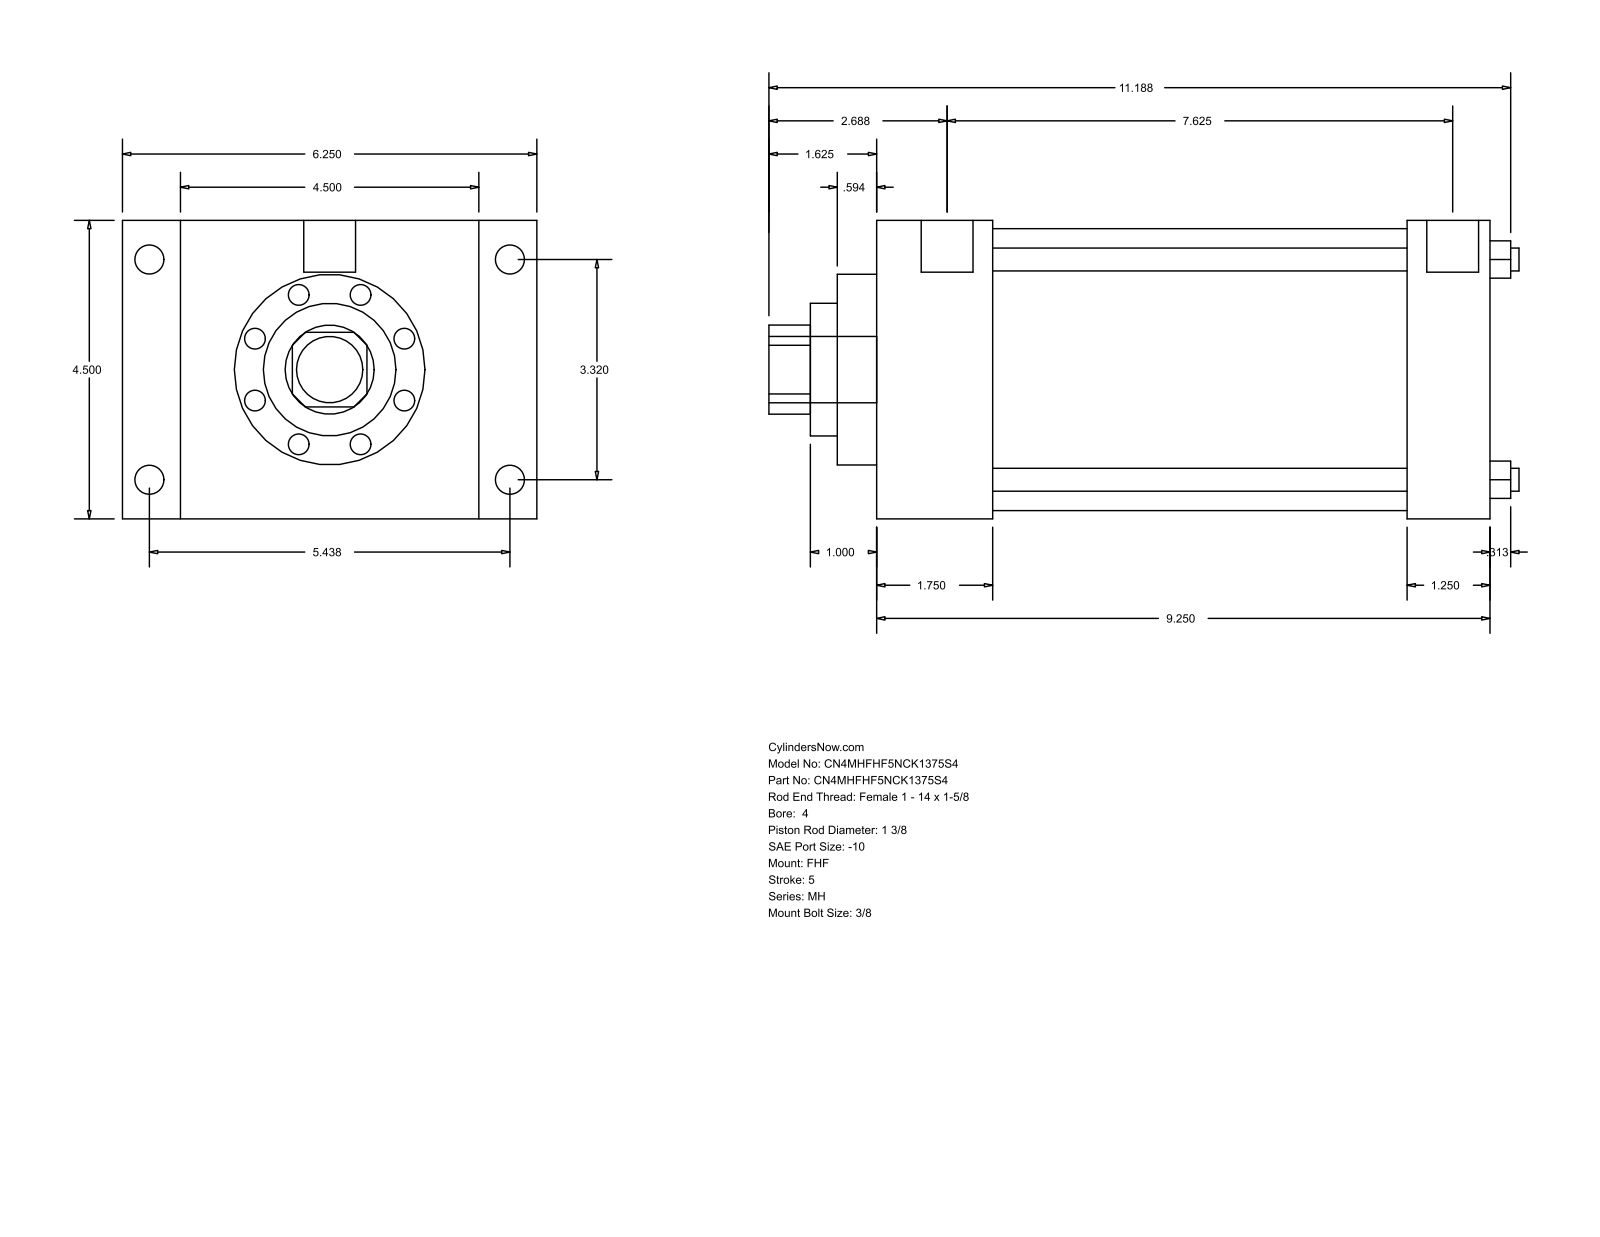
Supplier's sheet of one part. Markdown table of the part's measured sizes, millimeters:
| quantity | value |
| --- | --- |
| part name | MH_FHF__0400_1.375 |
| STEP written by | GSSL Pune (CONFIG_CONTROL_DESIGN) |
| units | millimeters |
| bodies | 0 solids, 90 faces (61 planar, 29 cylindrical, 0 other) |
| overall size | 287.34 × 158.75 × 114.3 |
| round holes (diameter × count) | 8.76 × 4, 34.92 × 1, 50.8 × 1, 73.03 × 1, 107.95 × 1 |
| round bosses / shafts (diameter × count) | 11.13 × 4, 8.73 × 4, 19.84 × 2, 25.4 × 1 |
| partial cylindrical surfaces (radius × count) | 17.06 × 1 |
| main face-to-face distances | 114.3, 234.96, 44.45, 190.51, 22.23, 136.53, 158.76, 158.75, 203.2, 31.76 |
| hole center spacings | 59.62, 84.32, 119.25 |
